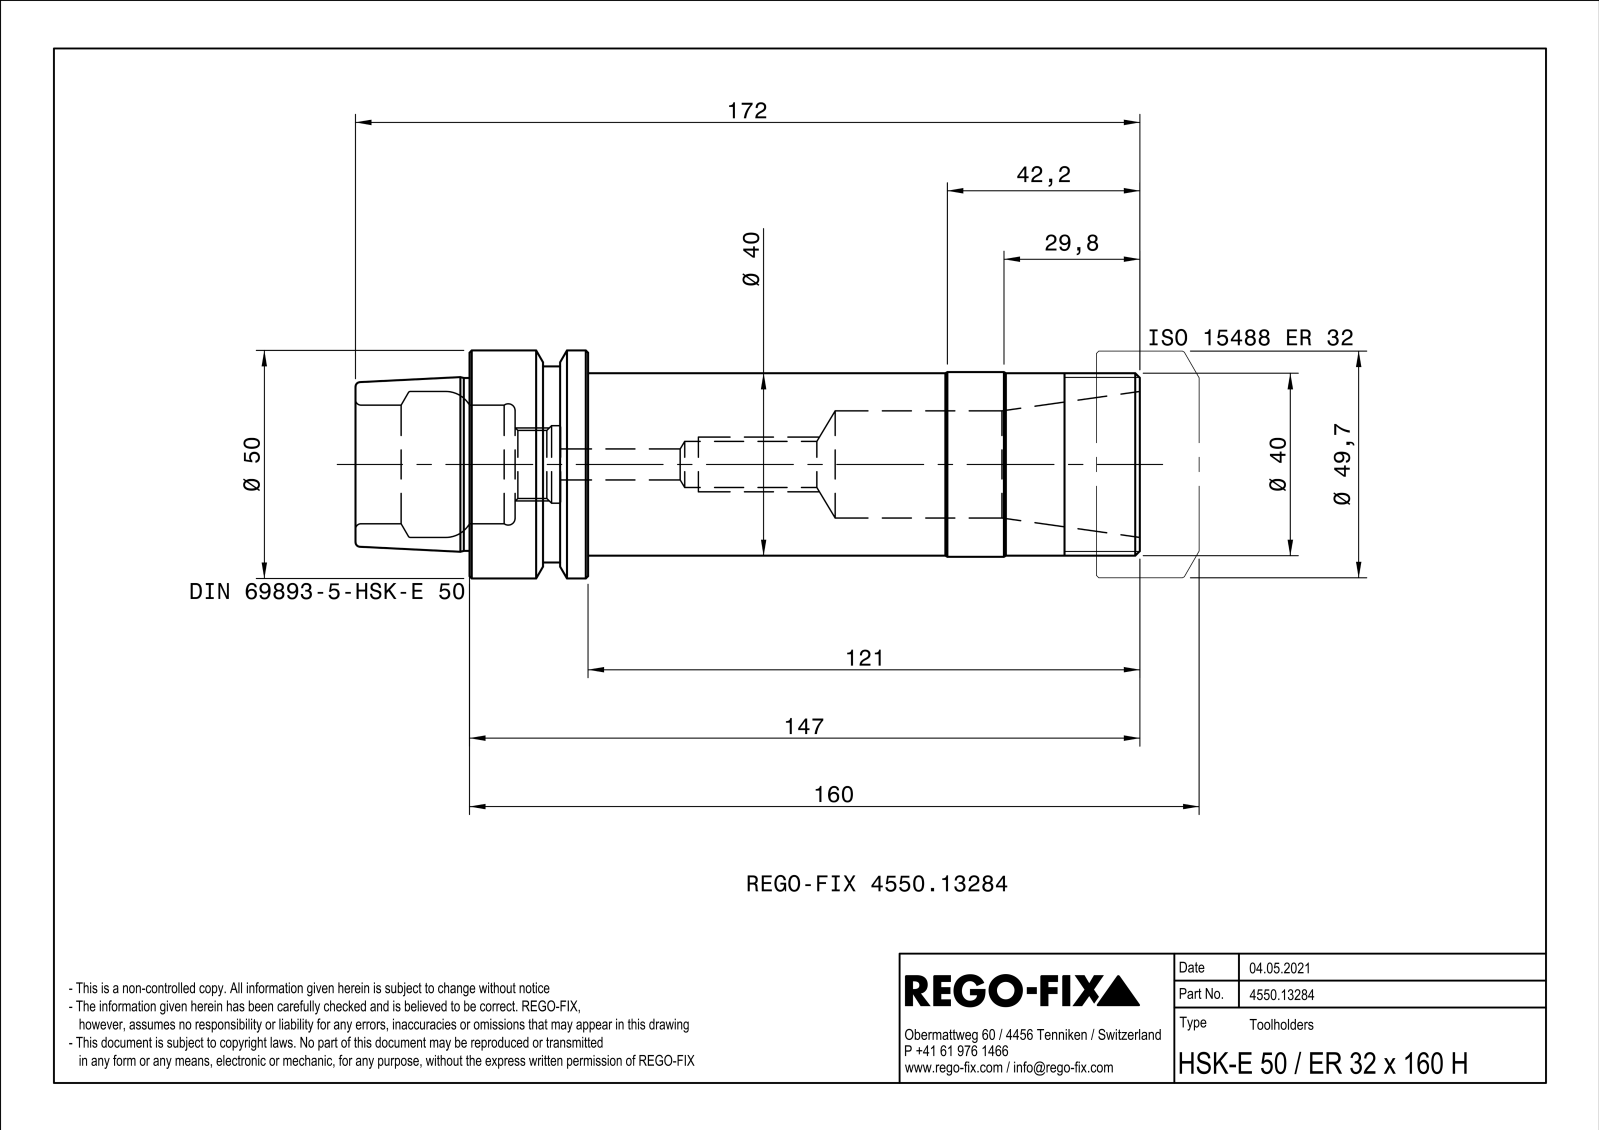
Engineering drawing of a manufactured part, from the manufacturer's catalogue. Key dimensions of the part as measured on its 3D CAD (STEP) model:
Part name (STEP PRODUCT): NOCUT
STEP written by: SIEMENS PLM Software Solid Edge ST10 (AUTOMOTIVE_DESIGN)
Units: millimetres
Bodies: 1 solid, 62 faces (8 planar, 20 cylindrical, 34 other)
Overall size (bounding box): 172 × 50 × 50
Volume: 165 368 mm³ · Surface area: 36 695 mm²
Round holes (diameter × count): ⌀6.8 ×1, ⌀10.11 ×1, ⌀14.92 ×1, ⌀17 ×1, ⌀23.5 ×1, ⌀26 ×1, ⌀32 ×1
Round bosses / shafts (diameter × count): ⌀50 ×1, ⌀43 ×1, ⌀40.5 ×1, ⌀40 ×1, ⌀39.3 ×1, ⌀38.01 ×1
Main face-to-face distances: 26, 10, 121, 147, 172, 51, 25, 137, 16, 35
